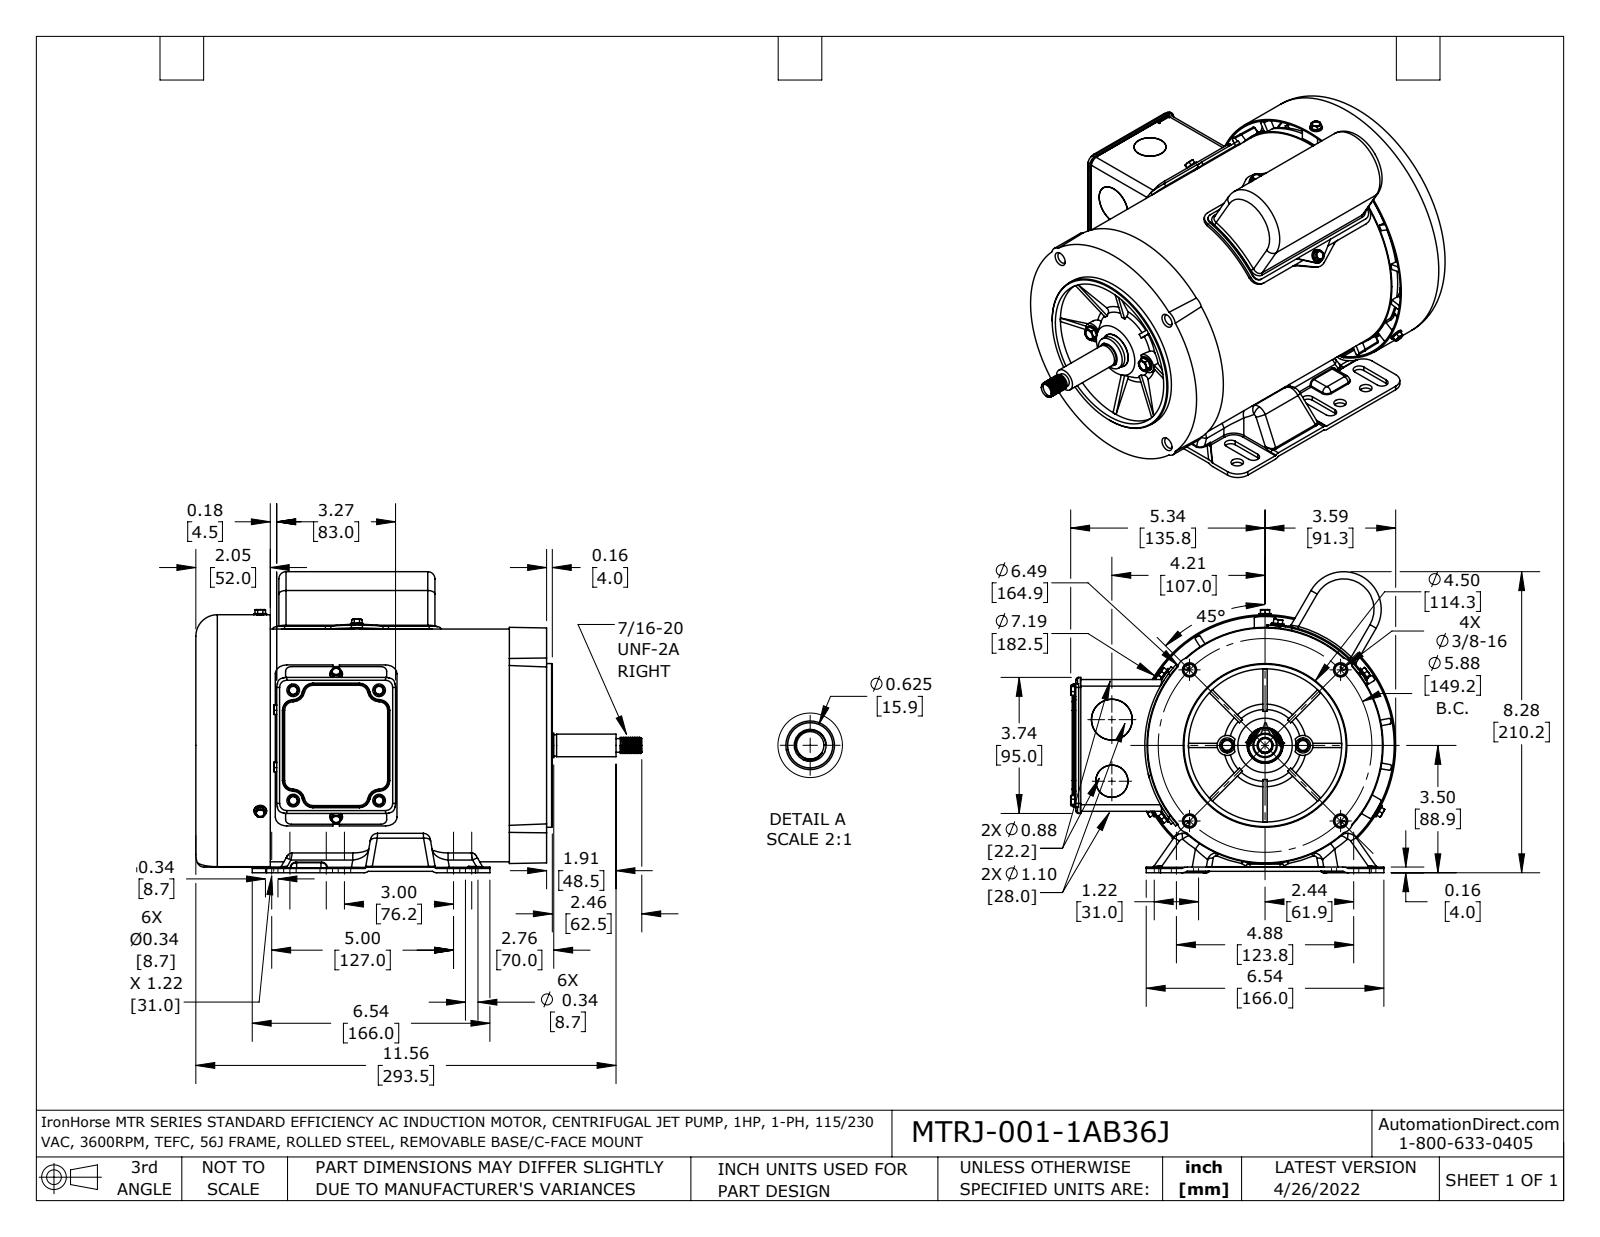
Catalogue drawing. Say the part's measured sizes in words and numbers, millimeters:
The part is named "MTRJ-001-1AB36J redcmb1 coord". Its 3-D file was written by "SolidWorks 2021 (AUTOMOTIVE_DESIGN)". It is 34 solids with 2940 faces: 731 planar, 966 cylindrical and 1243 other. Overall it measures 311.5 by 227 by 210.2 millimeters. Its volume is 779 900 cubic millimeters and its surface area 634 100 square millimeters. Round holes: 13 of diameter 5.6, 12 of diameter 5, 8 of diameter 7, 6 of diameter 4.5, 6 of diameter 5.5, 6 of diameter 8.3, 6 of diameter 8.7, 5 of diameter 3.5, 4 of diameter 3.8, 4 of diameter 8, 3 of diameter 18, 2 of diameter 3.3. Round bosses or shafts: 13 of diameter 4.2, 12 of diameter 8.8, 6 of diameter 6, 2 of diameter 10.5, 2 of diameter 4.8, 1 of diameter 182.5, 1 of diameter 162.5, 1 of diameter 114.3. Partial cylindrical surfaces (rounded edges, fillets, slot ends): 113 of radius 3, 57 of radius 1, 32 of radius 4, 30 of radius 0.5, 26 of radius 3.5, 20 of radius 5, 18 of radius 2, 18 of radius 7. The main face-to-face distances are 1, 3, 1.6, 0.8, 245, 244, 4, 90.4, 2, 78.4. The hole center spacings are 107.2, 77, 2.4, 58.9, 61.2, 74.6, 95.2, 97.6.
